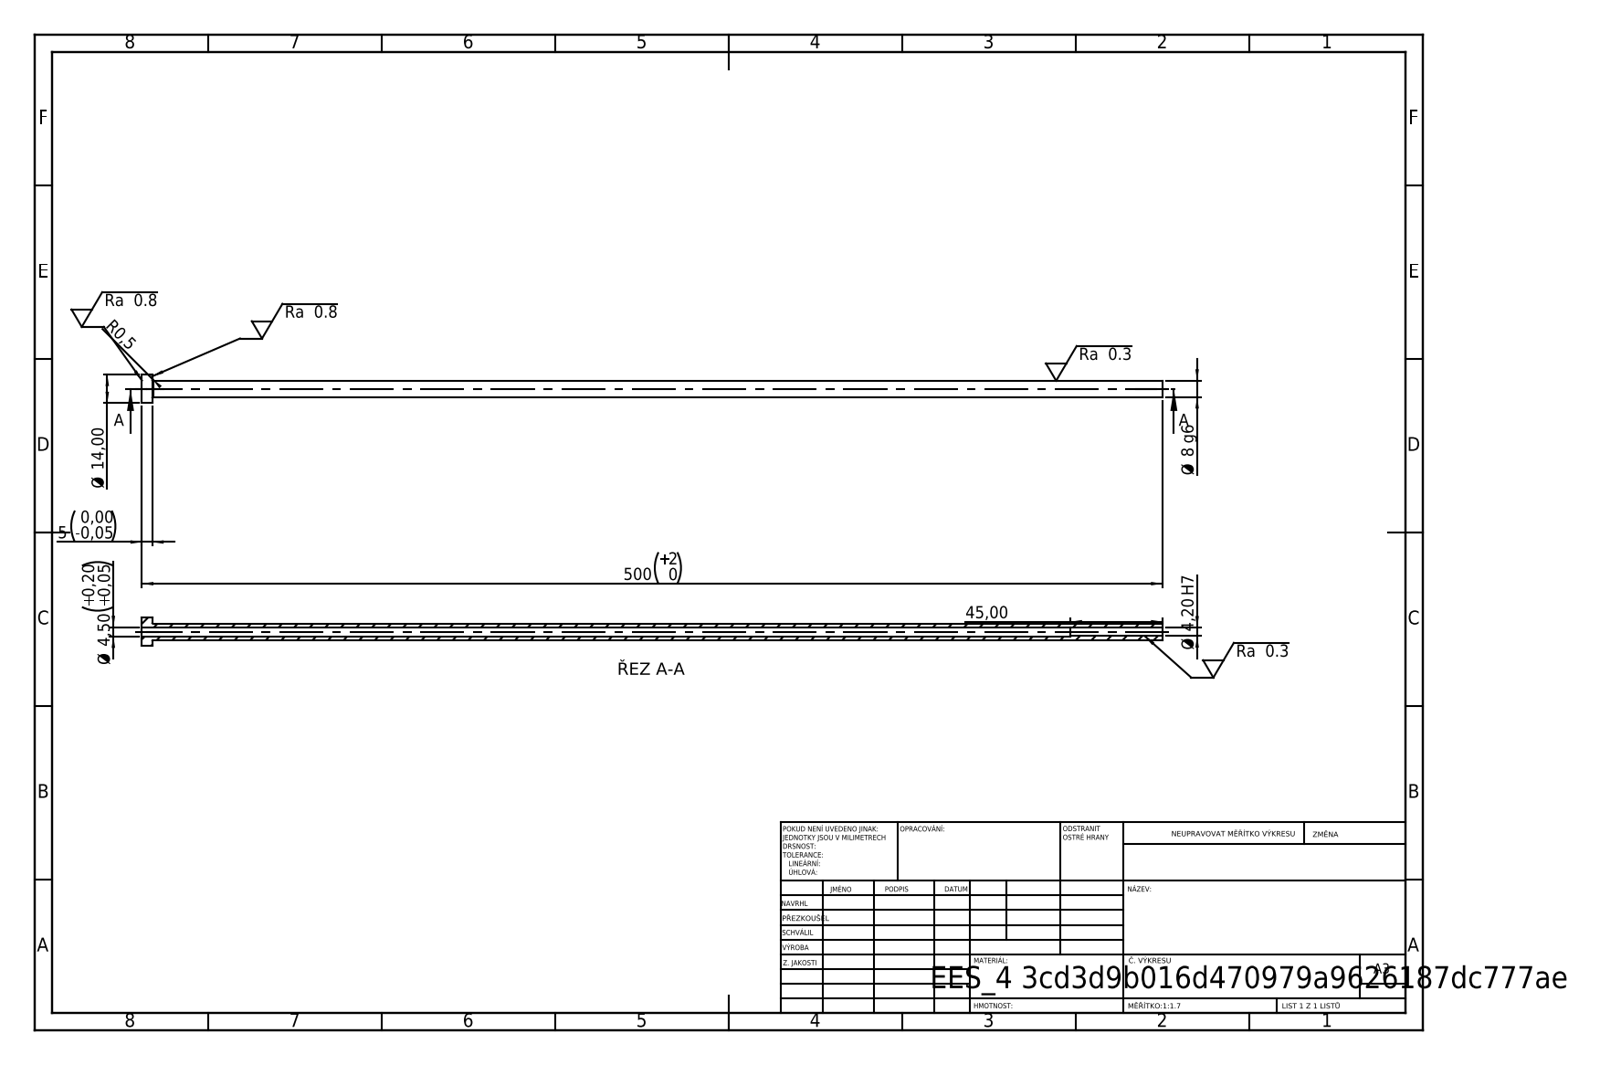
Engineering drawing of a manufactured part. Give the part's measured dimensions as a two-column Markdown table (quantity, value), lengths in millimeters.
| quantity | value |
| --- | --- |
| STEP written by | SolidWorks 2019 (CONFIG_CONTROL_DESIGN) |
| units | millimeters |
| bodies | 1 solid, 14 faces (4 planar, 8 cylindrical, 2 other) |
| overall size | 500 × 14 × 14 |
| volume | 17 793 mm³ |
| surface area | 19 962 mm² |
| round holes (diameter × count) | 4.2 × 1, 4.5 × 1 |
| round bosses / shafts (diameter × count) | 14 × 1, 8 × 1 |
| main face-to-face distances | 5, 500, 495, 455, 450, 45 |
